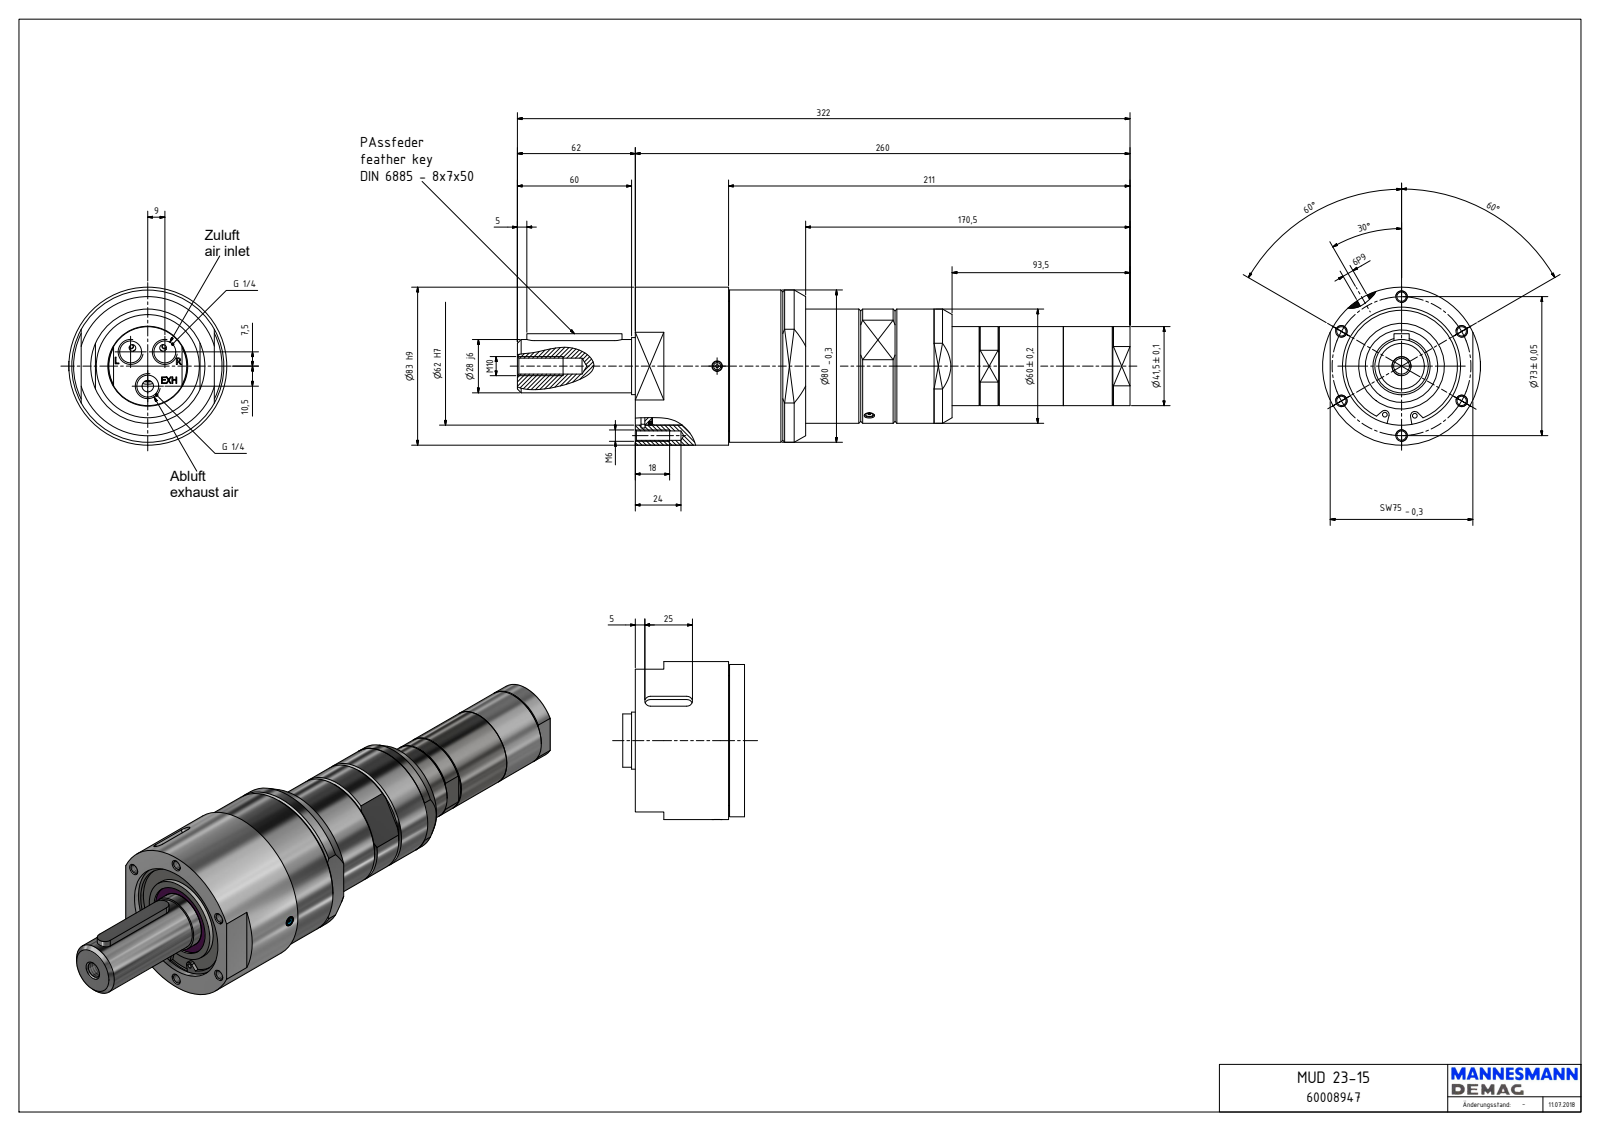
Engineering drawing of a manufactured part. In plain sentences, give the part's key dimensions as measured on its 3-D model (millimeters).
The part is named "MUD 23-15_60008947". Its 3-D file was written by "Autodesk Inventor 2018 (AUTOMOTIVE_DESIGN)". It is 1 solid with 243 faces: 124 planar, 62 cylindrical and 57 other. Overall it measures 322 by 83 by 83 millimeters. Its volume is 819 831 cubic millimeters and its surface area 76 893 square millimeters. Round holes: 6 of diameter 4.92, 3 of diameter 11.45, 2 of diameter 1.55, 2 of diameter 2.5, 2 of diameter 4, 2 of diameter 5.5, 1 of diameter 8.38, 1 of diameter 42, 1 of diameter 58.69, 1 of diameter 62, 1 of diameter 68.38. Round bosses or shafts: 2 of diameter 5, 2 of diameter 3.6, 1 of diameter 83, 1 of diameter 80, 1 of diameter 68.18, 1 of diameter 60, 1 of diameter 41.5, 1 of diameter 30. Partial cylindrical surfaces (rounded edges, fillets, slot ends): 2 of radius 2.25, 2 of radius 3, 2 of radius 4, 2 of radius 32.5, 1 of radius 25.37, 1 of radius 33.25. The main face-to-face distances are 4.62, 49, 44.38, 89.5, 84.88, 40.5, 0.5, 49.5, 44.88, 40. The hole center spacings are 36.5, 63.22, 73, 11.72, 20.12, 25.04, 26.98, 30.36.
